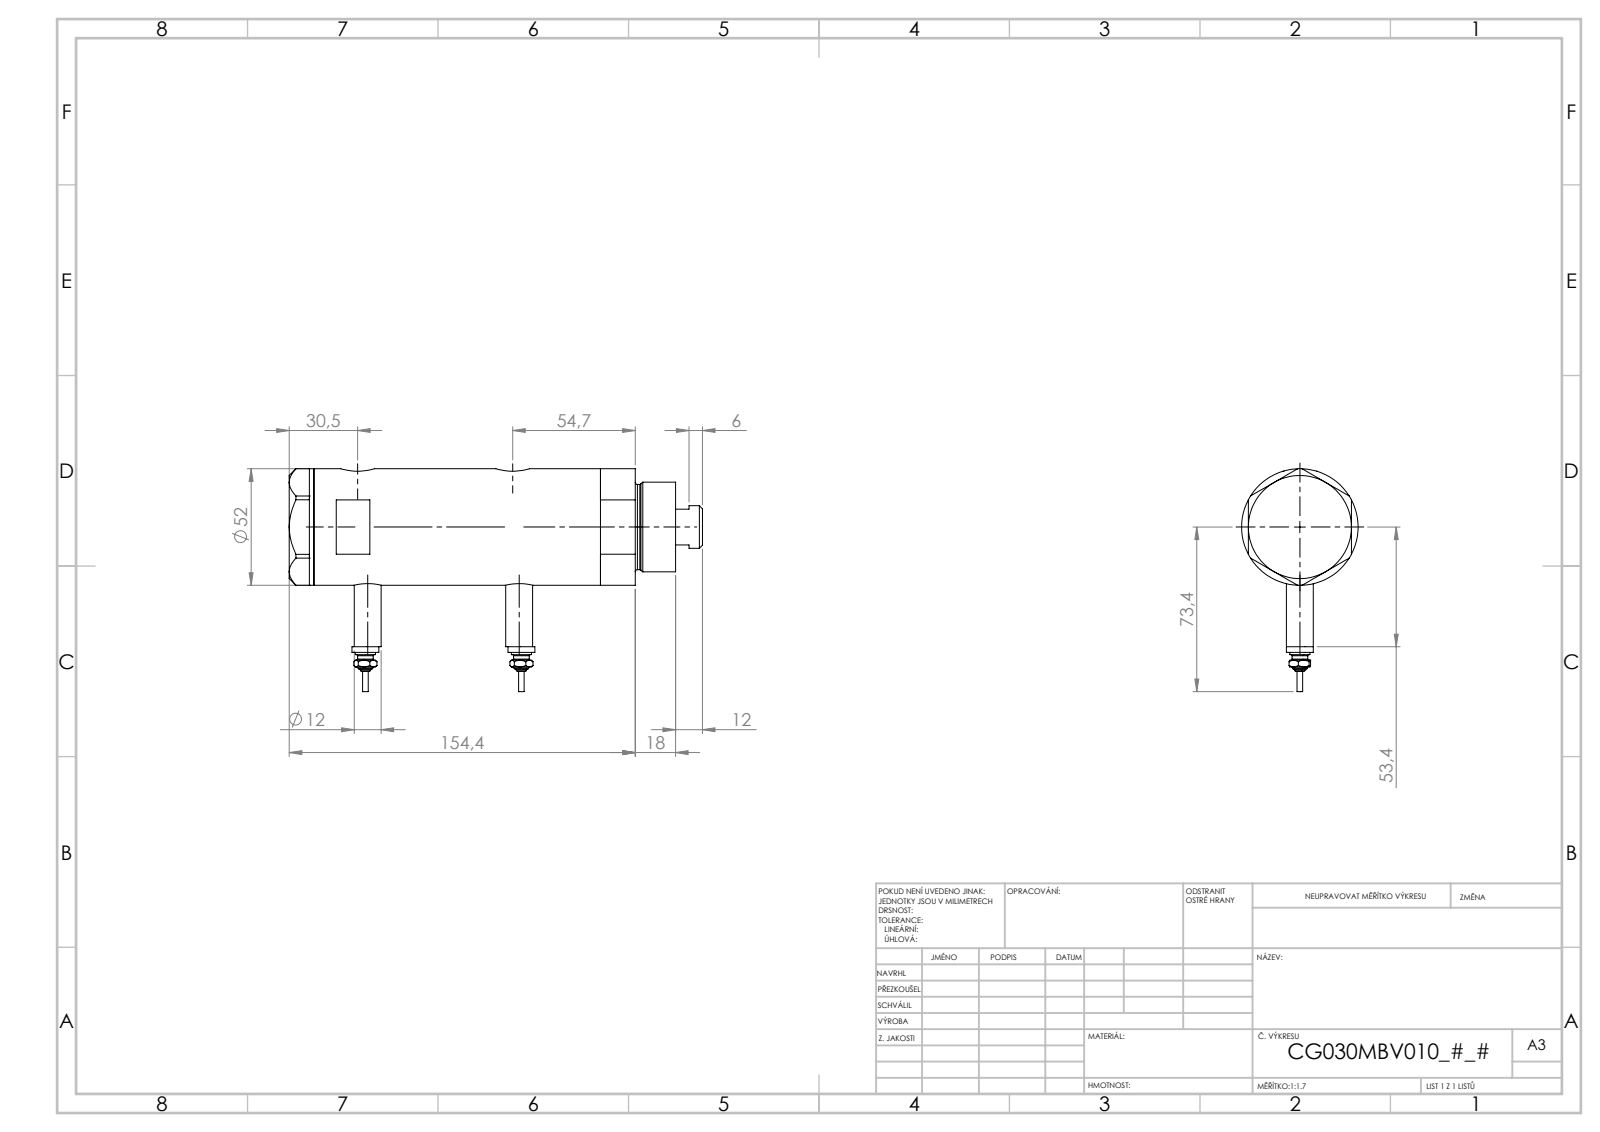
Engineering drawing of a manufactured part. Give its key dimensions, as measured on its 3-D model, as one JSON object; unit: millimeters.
{"part_name": "Switch; V270CG_FRONT; V270CG_BACK; V270CG_VC (+1 more)", "step_written_by": "SolidWorks 2019 (CONFIG_CONTROL_DESIGN)", "units": "millimeters", "bodies": {"solids": 6, "faces": 226, "planar": 93, "cylindrical": 69, "other": 64}, "overall_size": [184.4, 99.4, 52], "volume_mm3": 348788, "surface_area_mm2": 80541, "round_holes": [[9.73, 2], [12.5, 2], [15, 2], [6.5, 1], [20, 1], [21.5, 1], [30, 1], [33, 1], [44, 1]], "round_bosses_or_shafts": [[12, 4], [9, 2], [7, 2], [4.5, 2], [2.5, 2], [52, 1], [40, 1], [38, 1]], "face_to_face_distances": [91.5, 23.8, 67.7, 11, 34.8, 102.5, 46, 36.4, 138.9, 127.9], "hole_center_spacings": [2.9, 4.5, 64.7, 67.6, 69.2, 72.1]}
